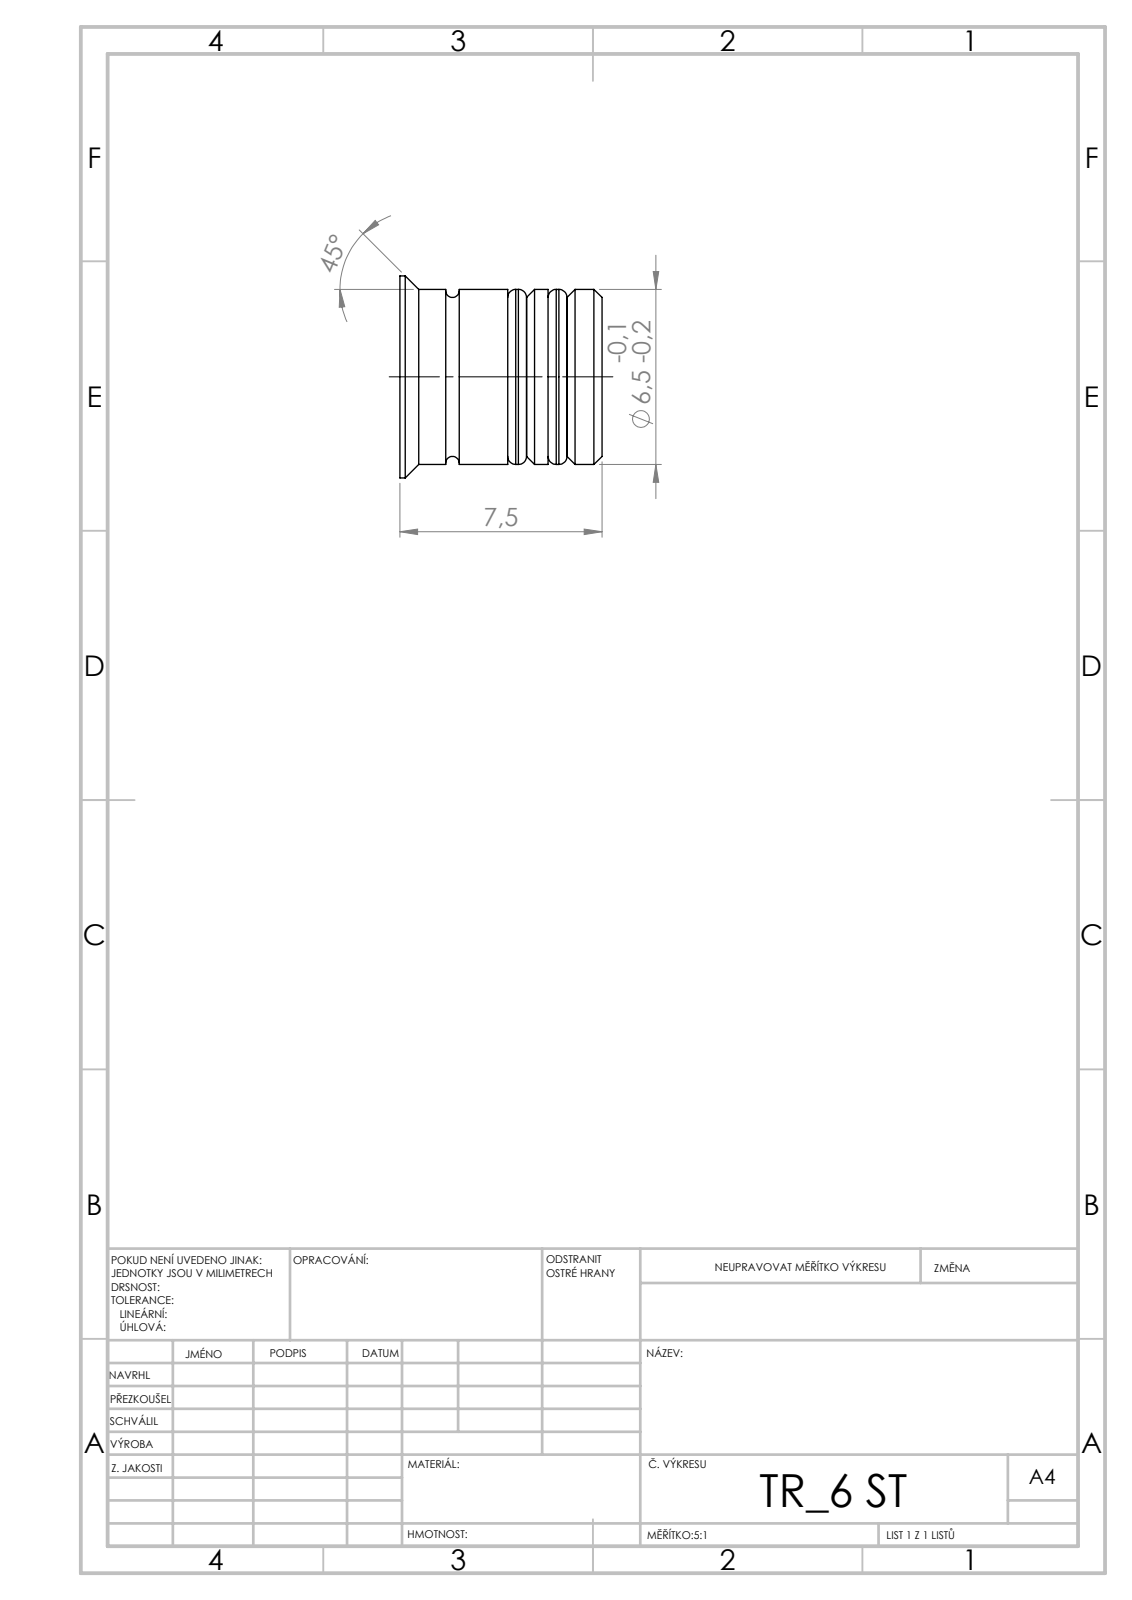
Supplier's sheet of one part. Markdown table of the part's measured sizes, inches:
| quantity | value |
| --- | --- |
| STEP written by | SolidWorks 2019 (CONFIG_CONTROL_DESIGN) |
| units | inches |
| bodies | 3 solids, 67 faces (25 planar, 20 cylindrical, 22 other) |
| overall size | 0.295 × 0.295 × 0.295 |
| volume | 0.017 in³ |
| surface area | 0.677 in² |
| round bosses / shafts (diameter × count) | 0.295 × 1, 0.256 × 1, 0.232 × 1, 0.138 × 1 |
| main face-to-face distances | 0.059, 0.028, 0.138, 0.157, 0.087, 0.217, 0.079, 0.295, 0.051, 0.11 |
